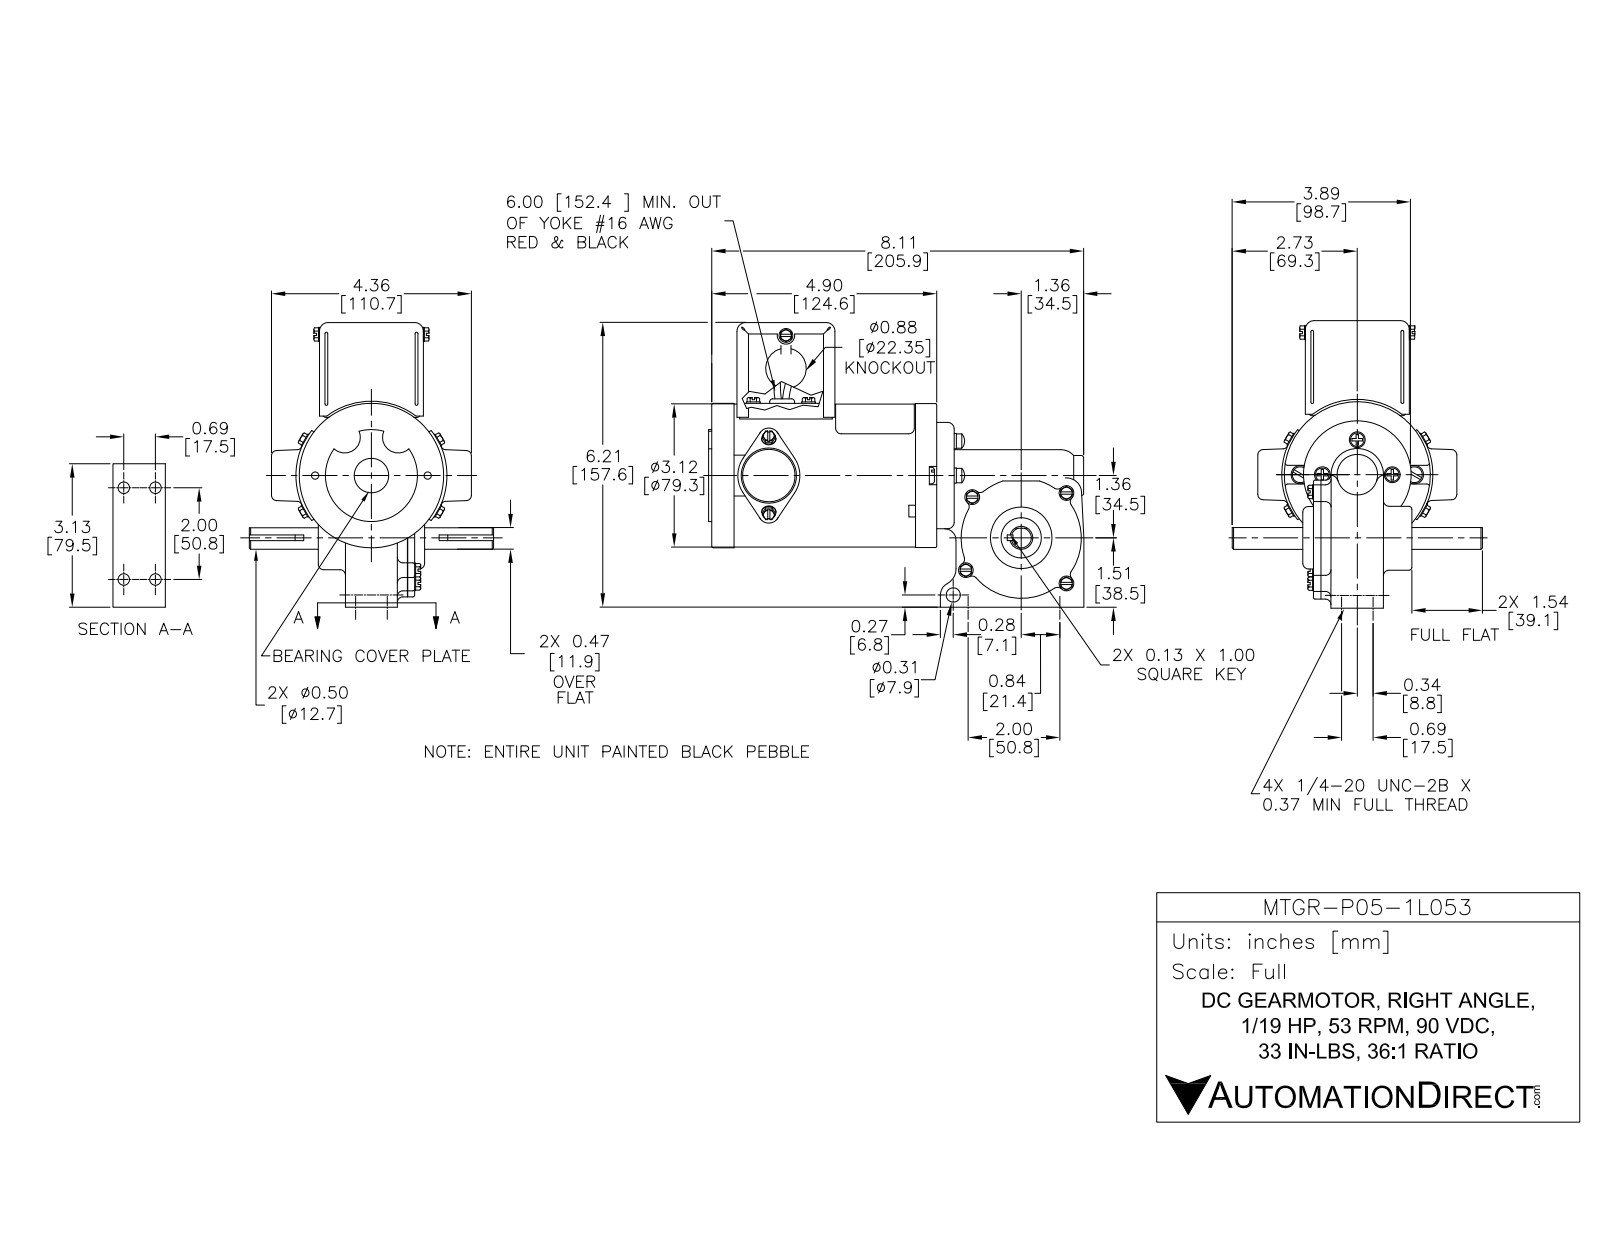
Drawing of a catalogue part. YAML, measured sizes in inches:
part_name: "P05-1L053"
step_written_by: "SolidWorks 2013 (AUTOMOTIVE_DESIGN)"
units: inches
bodies: {solids: 40, faces: 712, planar: 436, cylindrical: 210, other: 66}
overall_size: [8.179, 6.274, 5.453]
volume: 27.37
surface_area: 297.1
round_holes:
  - {diameter: 0.25, count: 5}
  - {diameter: 0.094, count: 2}
  - {diameter: 0.198, count: 2}
  - {diameter: 0.3, count: 1}
  - {diameter: 0.301, count: 1}
  - {diameter: 0.375, count: 1}
  - {diameter: 0.5, count: 1}
  - {diameter: 0.86, count: 1}
  - {diameter: 1.225, count: 1}
  - {diameter: 3, count: 1}
  - {diameter: 3.125, count: 1}
round_bosses_or_shafts:
  - {diameter: 0.321, count: 4}
  - {diameter: 0.3, count: 4}
  - {diameter: 0.346, count: 3}
  - {diameter: 0.295, count: 3}
  - {diameter: 0.125, count: 2}
  - {diameter: 0.1, count: 2}
  - {diameter: 3.156, count: 1}
  - {diameter: 3.14, count: 1}
partial_cylinders:
  - {radius: 0.1, count: 10}
  - {radius: 0.191, count: 4}
  - {radius: 0.234, count: 4}
  - {radius: 0.15, count: 2}
  - {radius: 0.159, count: 2}
  - {radius: 0.341, count: 2}
  - {radius: 0.25, count: 1}
  - {radius: 0.34, count: 1}
face_to_face_distances: [0.031, 0.25, 0.063, 4.65, 2.135, 0.307, 2.047, 1.67, 1.608, 0.245]
hole_center_spacings: [0.343, 0.456, 0.686, 1.23, 2, 2.029, 2.114, 2.326]
